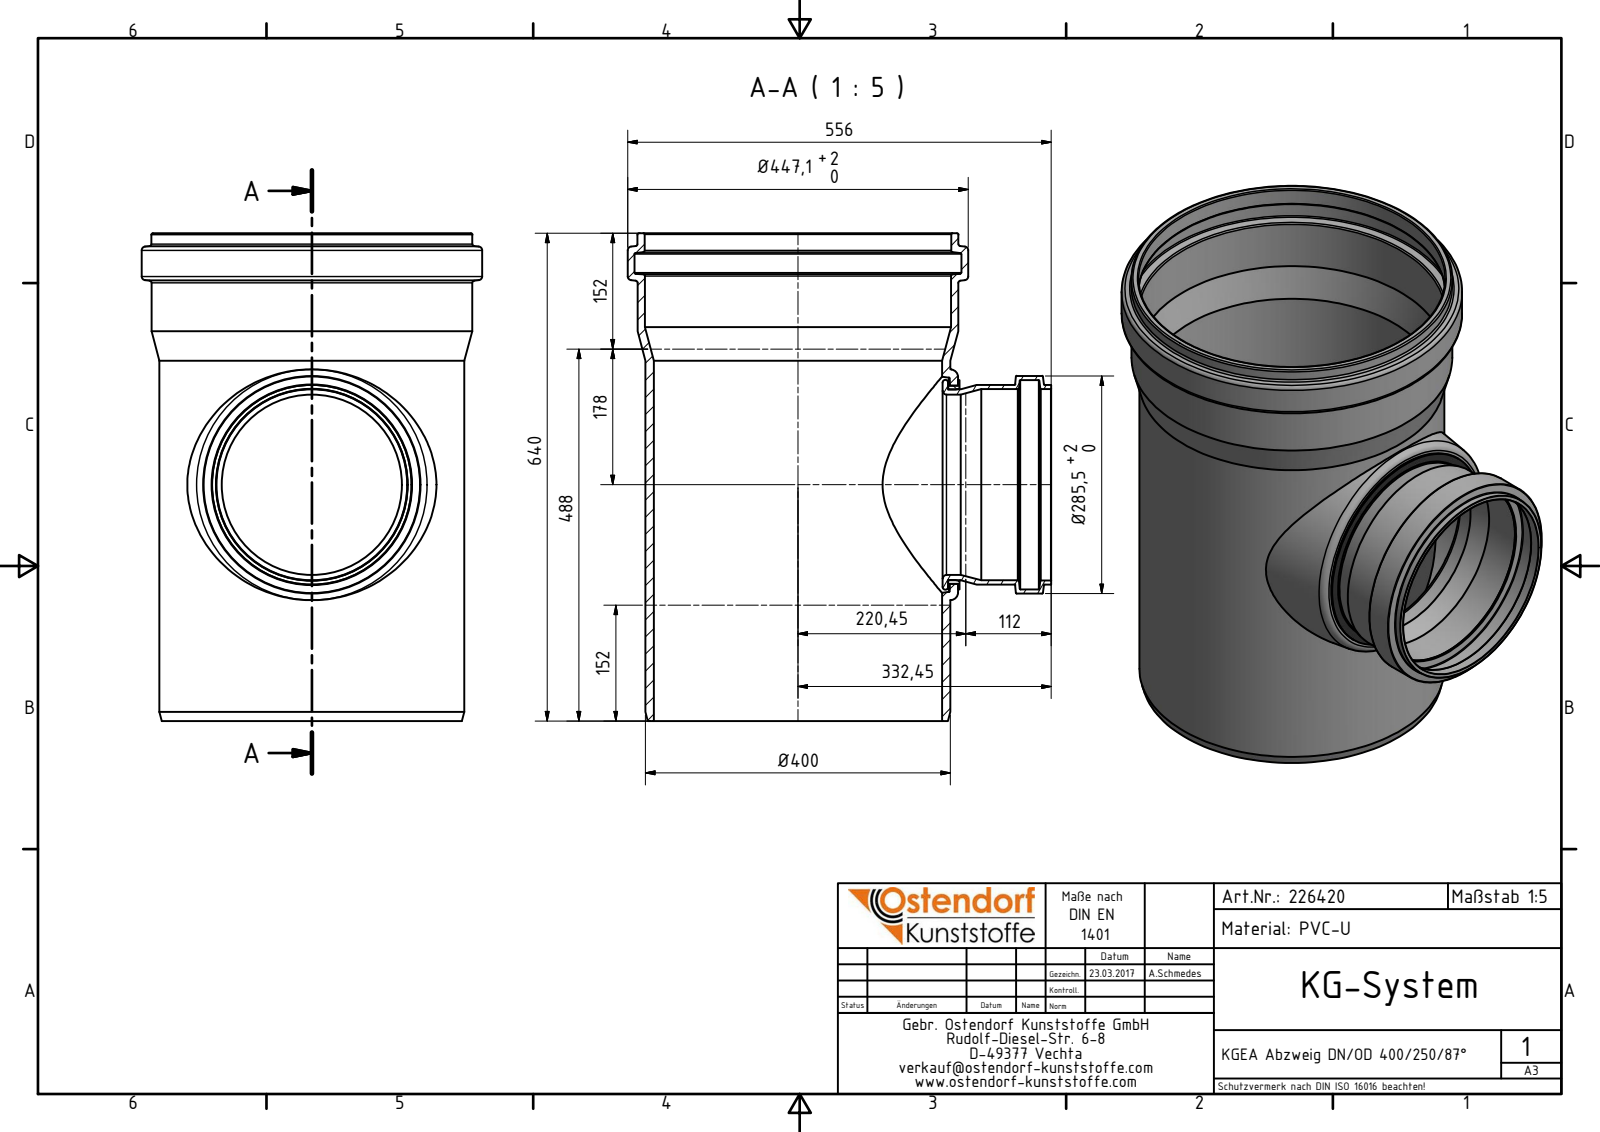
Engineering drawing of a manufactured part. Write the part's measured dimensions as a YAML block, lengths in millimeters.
part_name: "226420 KGEA Abzweig DN_OD 400_250_87°; 226420 KGEA Abzweig DN_OD 400_200_87° Dichtung; 226420 KGEA Abzweig DN_OD 400_250_87° Abzweig"
step_written_by: "Autodesk Inventor 2016 (AUTOMOTIVE_DESIGN)"
units: millimeters
bodies: {solids: 3, faces: 74, planar: 12, cylindrical: 22, other: 40}
overall_size: [640, 556, 447.1]
volume: 9400000
surface_area: 1975000
round_holes:
  - {diameter: 236.3, count: 1}
  - {diameter: 250, count: 1}
  - {diameter: 250.8, count: 1}
  - {diameter: 251.1, count: 1}
  - {diameter: 260, count: 1}
  - {diameter: 378.35, count: 1}
  - {diameter: 402, count: 1}
  - {diameter: 402.4, count: 1}
  - {diameter: 429.1, count: 1}
round_bosses_or_shafts:
  - {diameter: 447.1, count: 1}
  - {diameter: 421.4, count: 1}
  - {diameter: 421.1, count: 1}
  - {diameter: 400.35, count: 1}
  - {diameter: 285.5, count: 1}
  - {diameter: 274.5, count: 1}
  - {diameter: 262.1, count: 1}
  - {diameter: 261.8, count: 1}
face_to_face_distances: [13, 2, 11, 15, 7.1, 9.1, 20.1, 22.1, 640, 142.37]
